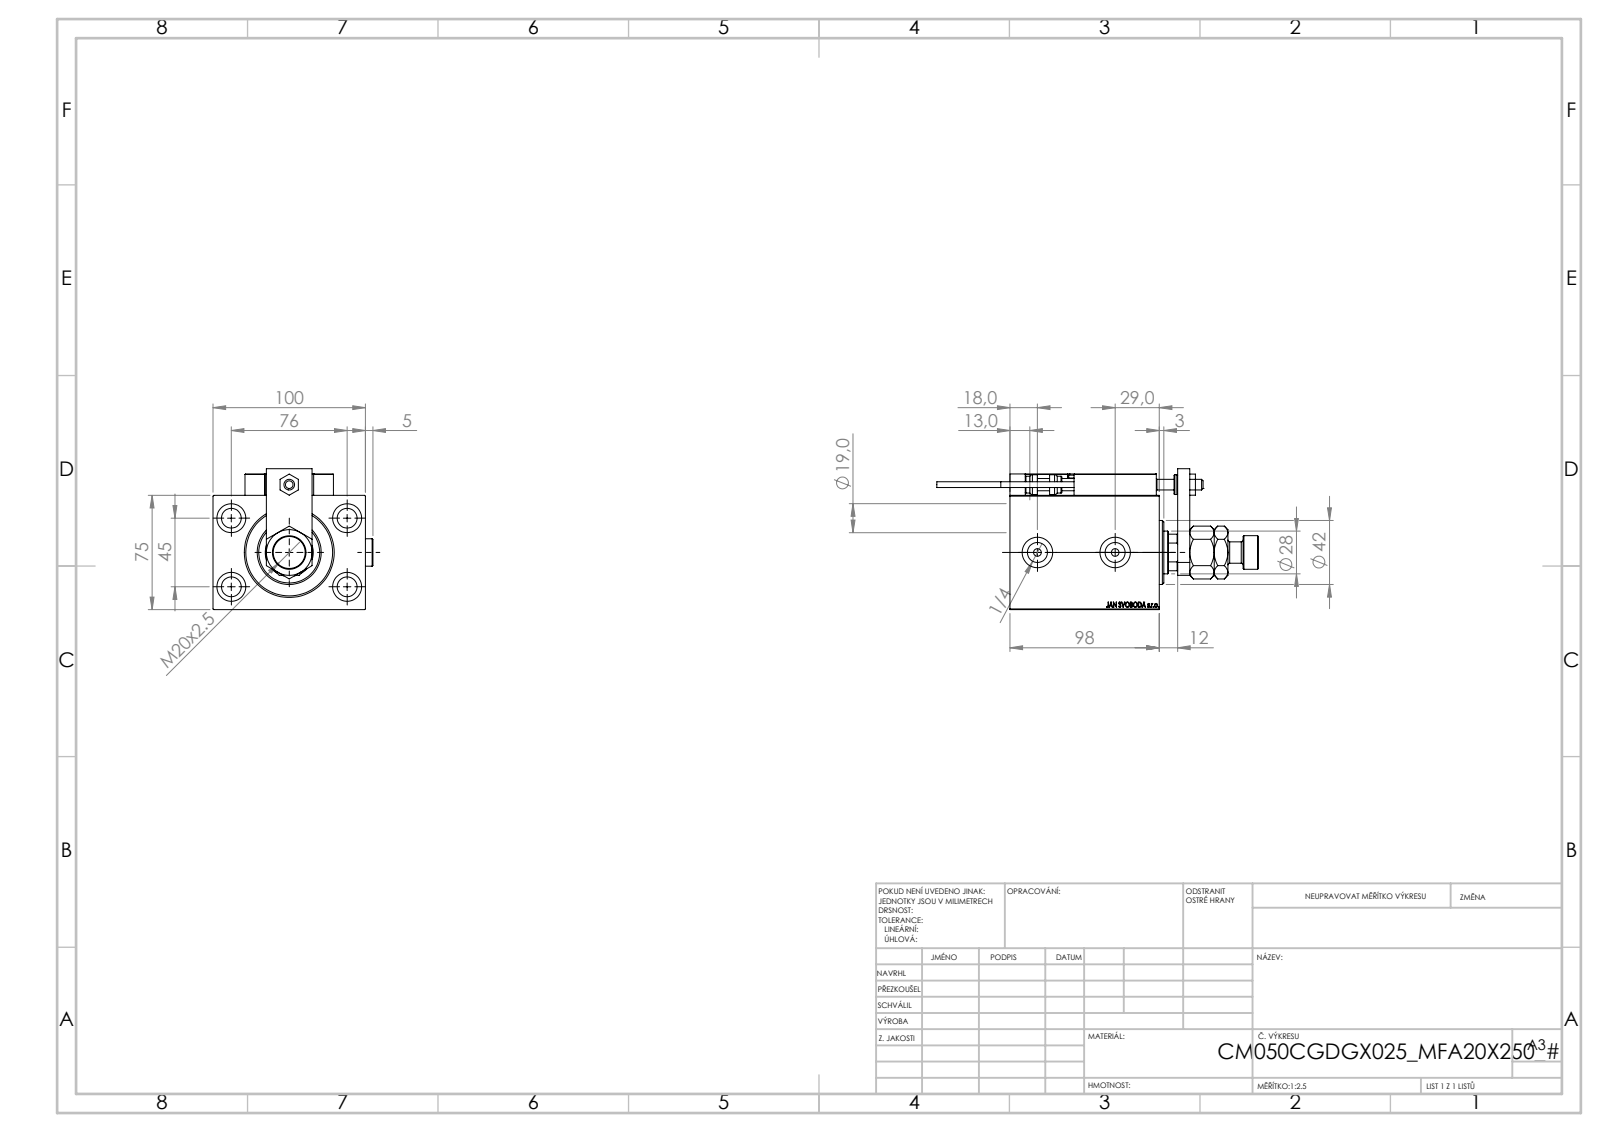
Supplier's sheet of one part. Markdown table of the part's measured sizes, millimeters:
| quantity | value |
| --- | --- |
| part name | ZARAZKA; ALLEN BOLT D5; KONCOVKA; NUT_D12 (+8 more) |
| STEP written by | SolidWorks 2019 (CONFIG_CONTROL_DESIGN) |
| units | millimeters |
| bodies | 26 solids, 1391 faces (611 planar, 210 cylindrical, 570 other) |
| overall size | 211 × 104.9 × 92.5 |
| volume | 709 320 mm³ |
| surface area | 140 820 mm² |
| round holes (diameter × count) | 8 × 5, 3.2 × 4, 4 × 4, 5 × 4, 13 × 4, 19 × 4, 20 × 3, 13.16 × 2, 7 × 1, 18.5 × 1, 28 × 1, 31.5 × 1 |
| round bosses / shafts (diameter × count) | 18 × 2, 5 × 2, 3.8 × 2, 42 × 1, 22 × 1, 14 × 1, 13 × 1, 11 × 1 |
| partial cylindrical surfaces (radius × count) | 0.3 × 30, 3 × 2, 13.5 × 1 |
| main face-to-face distances | 75, 14, 100, 98, 12, 25, 32, 84, 20, 24 |
| hole center spacings | 44.16, 11.37, 20, 29.59, 29.69, 36.06, 42.19, 43.91 |
